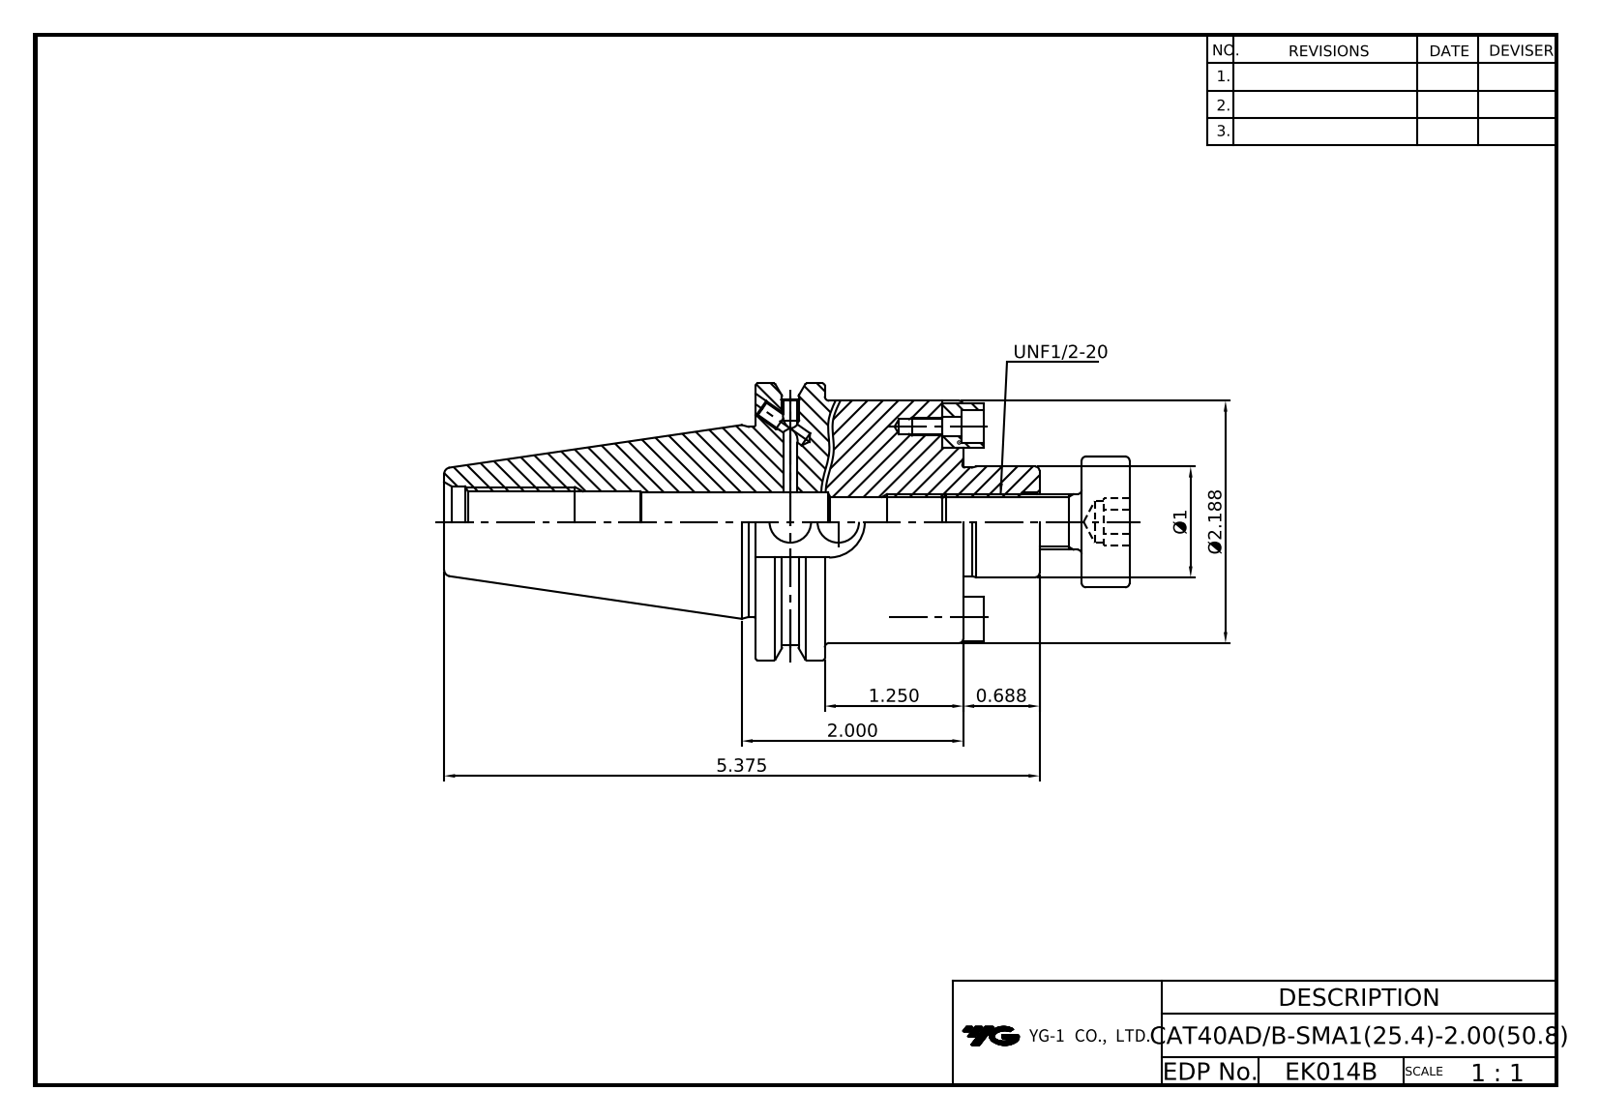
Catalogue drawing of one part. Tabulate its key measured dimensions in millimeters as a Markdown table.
| quantity | value |
| --- | --- |
| part name | LO-CAT40ADB-SMA25.4-50.8; HEX'' WRENCH BOLT-UNC#8-32x3_8L; DRIVE KEY-9.52x9.52x10.2; COLLAR BOLT-UNF1_2-20x32L |
| STEP written by | Autodesk Inventor 2022 (AUTOMOTIVE_DESIGN) |
| units | millimeters |
| bodies | 6 solids, 171 faces (85 planar, 48 cylindrical, 38 other) |
| overall size | 159.2 × 63.5 × 61.1 |
| volume | 192 100 mm³ |
| surface area | 35 780 mm² |
| round holes (diameter × count) | 3.3 × 4, 3.3 × 2, 4 × 2, 4.2 × 2, 4.5 × 2, 7.5 × 2, 9.5 × 2, 11.3 × 1, 13 × 1, 13.4 × 1, 13.5 × 1, 16.3 × 1 |
| round bosses / shafts (diameter × count) | 6.9 × 2, 4.2 × 2, 63.5 × 1, 55.6 × 1, 43.6 × 1, 30 × 1, 25.4 × 1, 12.7 × 1 |
| partial cylindrical surfaces (radius × count) | 4.7 × 2, 8.2 × 1, 28.1 × 1 |
| main face-to-face distances | 47.6, 87.8, 40.1, 76.8, 29.1, 11, 9.5, 42.8, 4.8, 33.9 |
| hole center spacings | 20.9, 41.7 |
